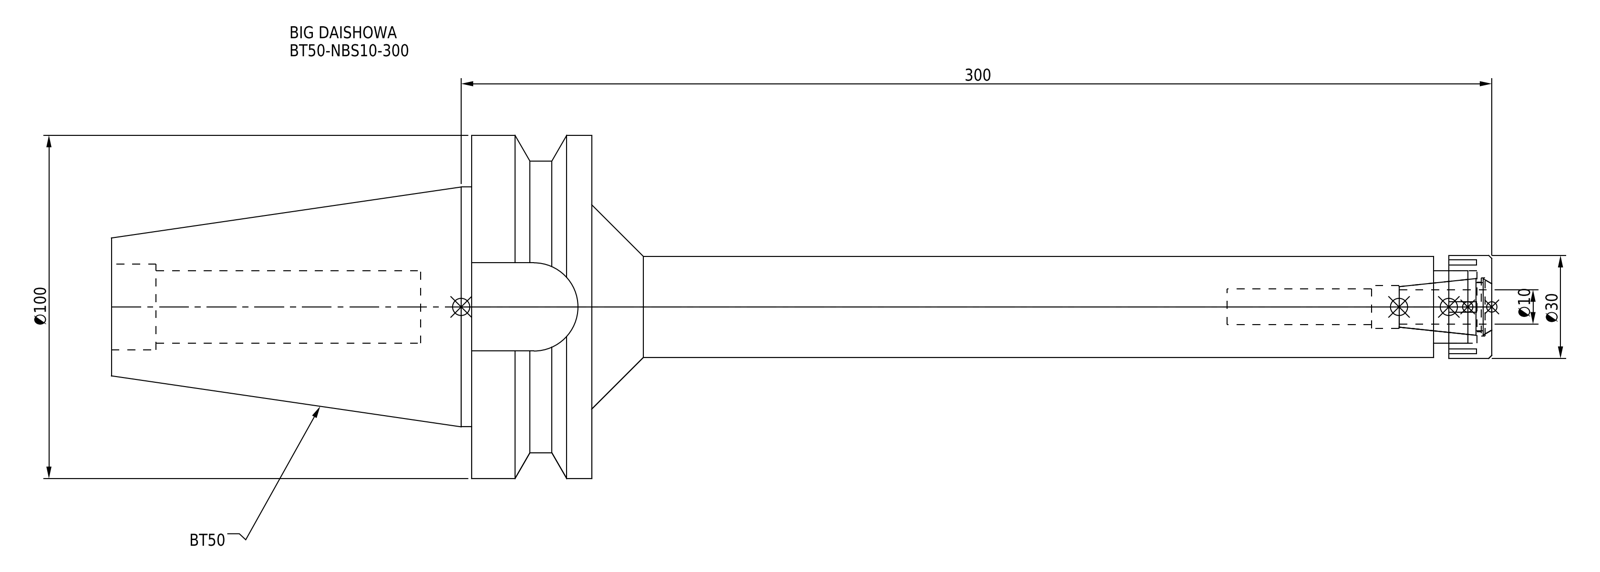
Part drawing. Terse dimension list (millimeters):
name: BT50-NBS10-300.stp; BT50-NBS10-300-FreeParts; BT50-NBS10-300; DXF_TEMP_ASSY_ASM_4_ASM.stp (+3 more)
written by: SolidWorks 2019 (CONFIG_CONTROL_DESIGN)
unit: mm
bodies: 2 solids, 89 faces (45 planar, 30 cylindrical, 14 other)
size: 401.8 × 100 × 100
volume: 642 638 mm³; area: 79 899 mm²
holes: 1× ⌀10.4, 1× ⌀12.5, 1× ⌀14.5, 1× ⌀17, 1× ⌀21, 1× ⌀21.2, 1× ⌀25
bosses: 1× ⌀100, 1× ⌀85, 1× ⌀69.85, 1× ⌀30, 1× ⌀29.5
rounds: 1× R12.85
face distances: 35, 139.8, 104.8, 70.8, 262, 297, 401.8, 311.8, 25.7, 4.5
